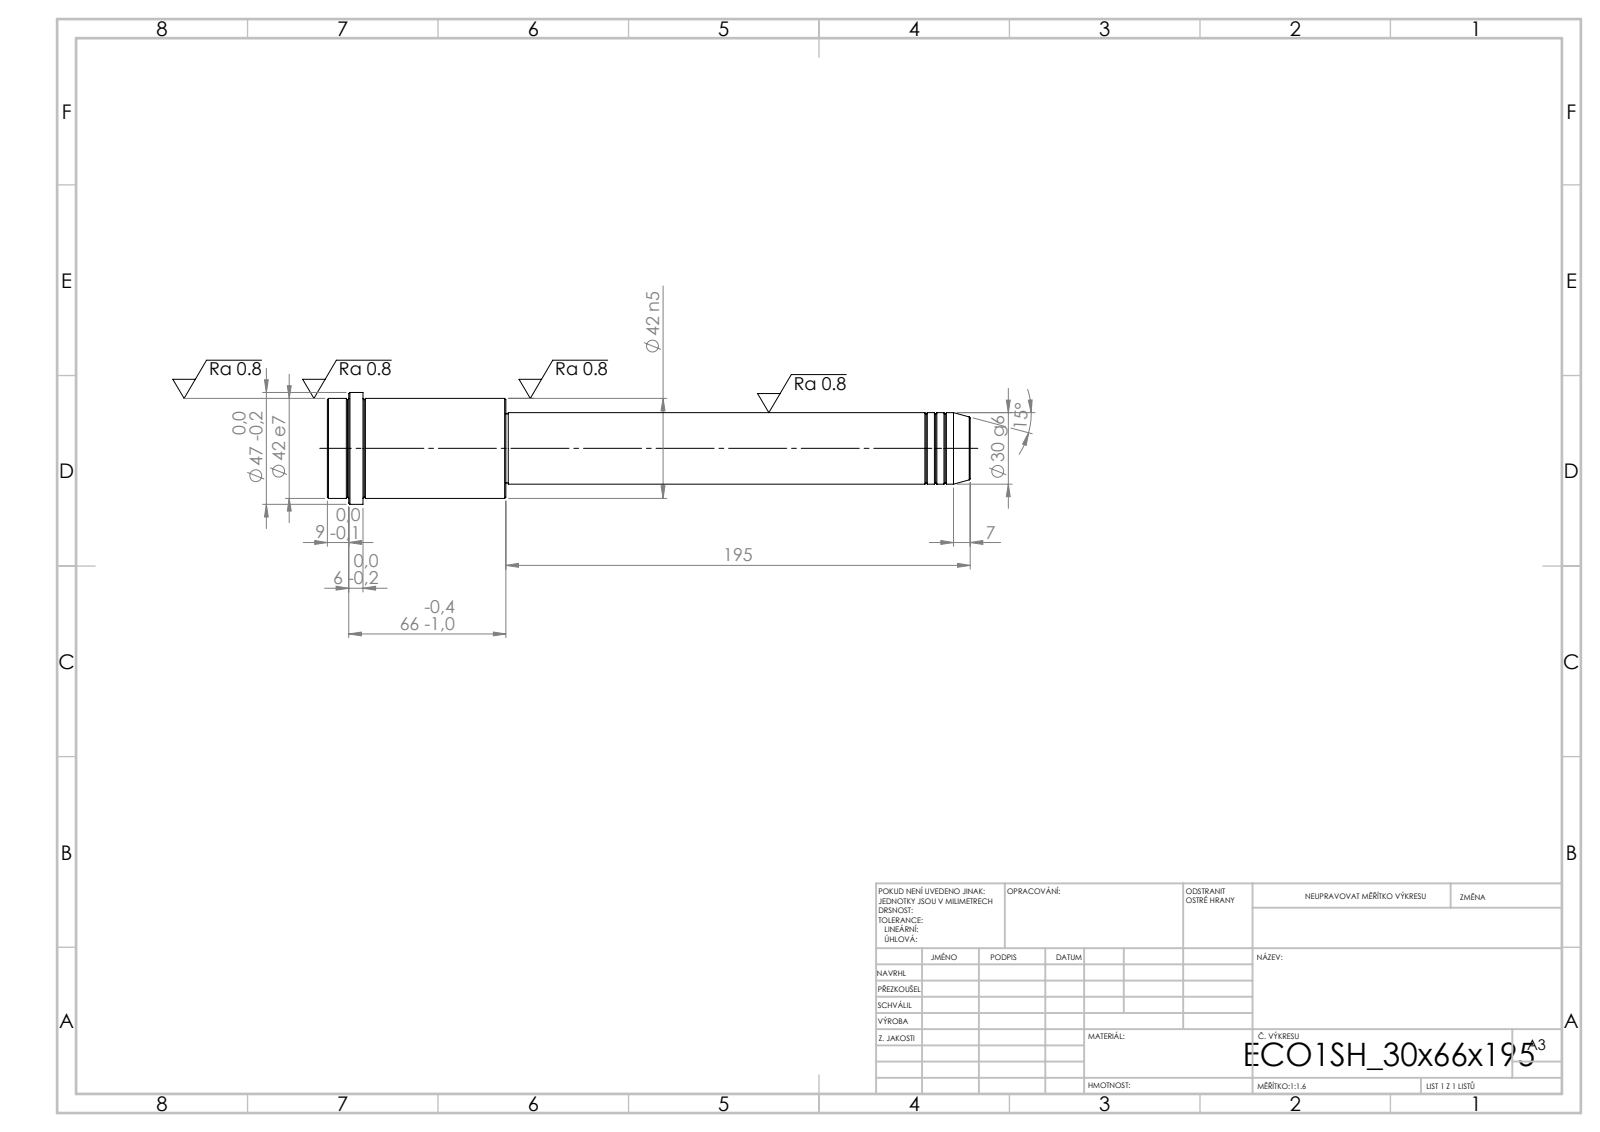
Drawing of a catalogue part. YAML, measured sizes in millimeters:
step_written_by: "SolidWorks 2019 (CONFIG_CONTROL_DESIGN)"
units: millimeters
bodies: {solids: 1, faces: 52, planar: 6, cylindrical: 16, other: 30}
overall_size: [270, 47, 47]
volume: 242938
surface_area: 31908
round_bosses_or_shafts:
  - {diameter: 47, count: 1}
  - {diameter: 42, count: 1}
  - {diameter: 30, count: 1}
  - {diameter: 29, count: 1}
face_to_face_distances: [75, 195, 270, 255, 60, 15, 261, 66, 6, 9]
